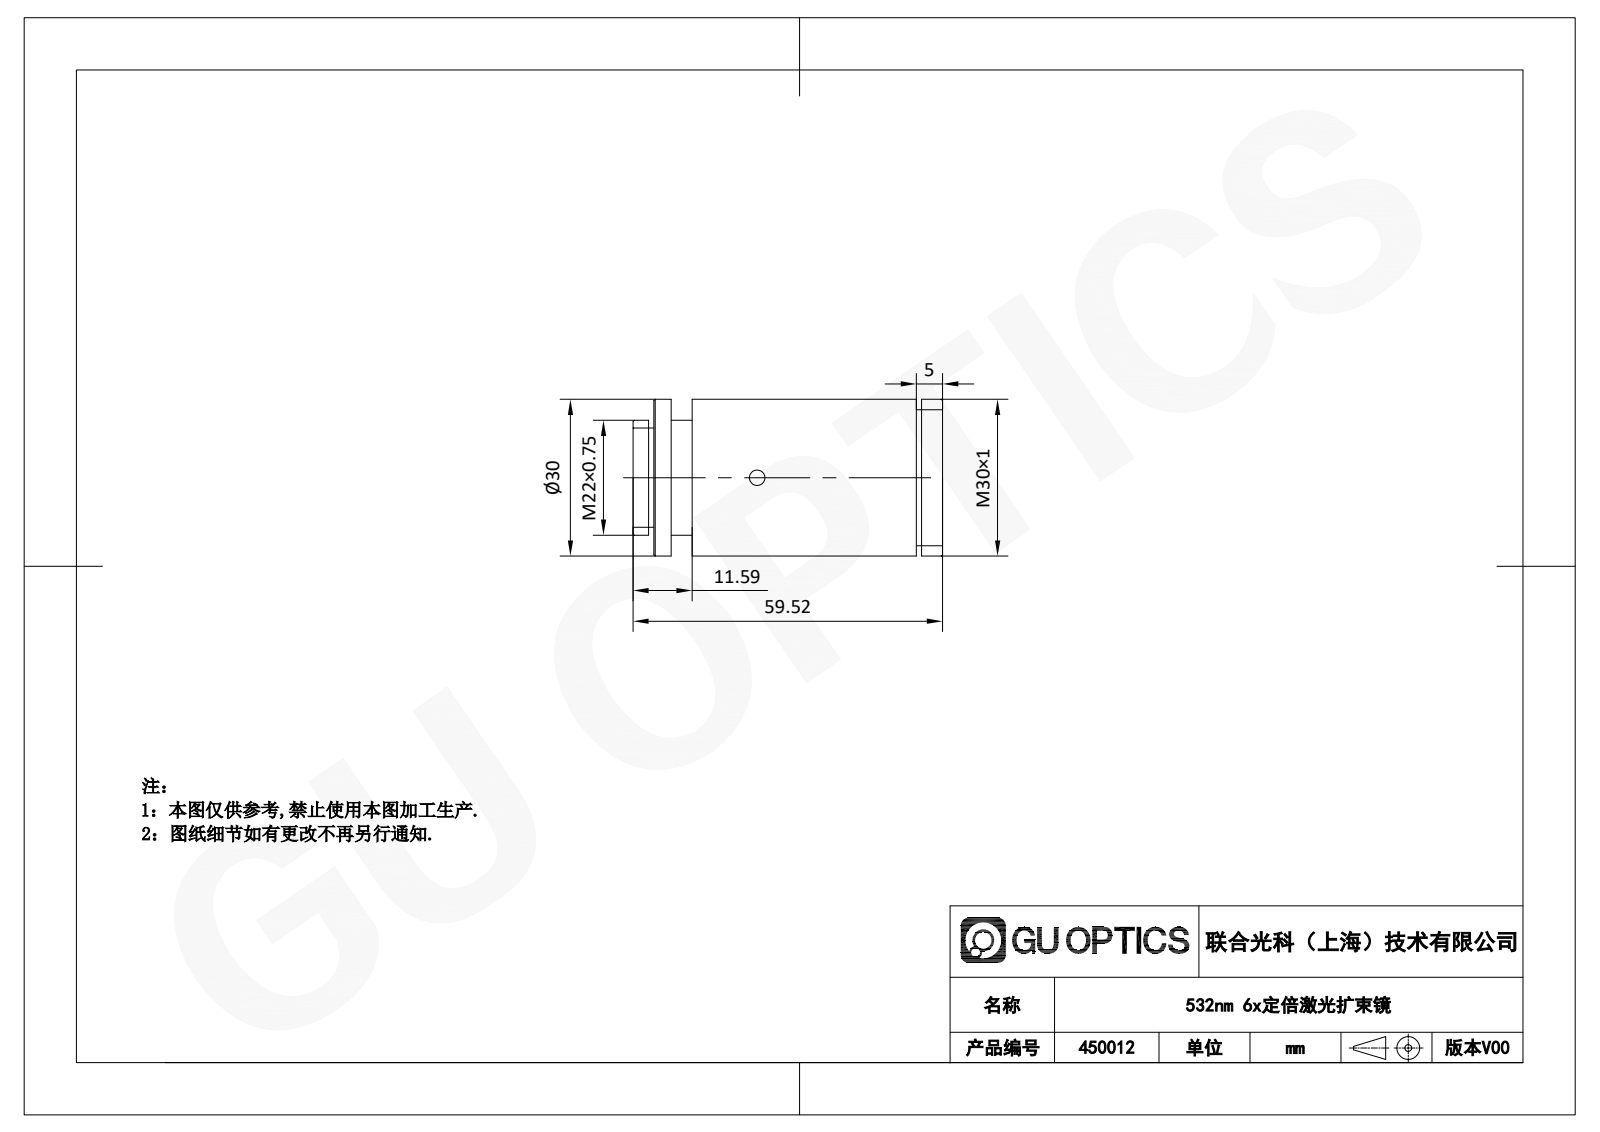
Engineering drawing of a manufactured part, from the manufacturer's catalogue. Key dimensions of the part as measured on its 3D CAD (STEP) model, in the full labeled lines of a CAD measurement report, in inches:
Part name (STEP PRODUCT): 450012
STEP written by: SolidWorks 2020 (AUTOMOTIVE_DESIGN)
Units: inches
Bodies: 1 solid, 43 faces (11 planar, 22 cylindrical, 10 other)
Overall size (bounding box): 2.343 × 1.181 × 1.181
Volume: 1.951 in³ · Surface area: 16.46 in²
Round holes (diameter × count): ⌀0.315 ×1, ⌀0.709 ×1
Round bosses / shafts (diameter × count): ⌀1.181 ×1, ⌀1.024 ×1, ⌀0.866 ×1, ⌀0.748 ×1
Main face-to-face distances: 0.157, 2.186, 1.887, 0.299, 2.028, 0.141, 2.044, 1.73, 0.039, 0.456
